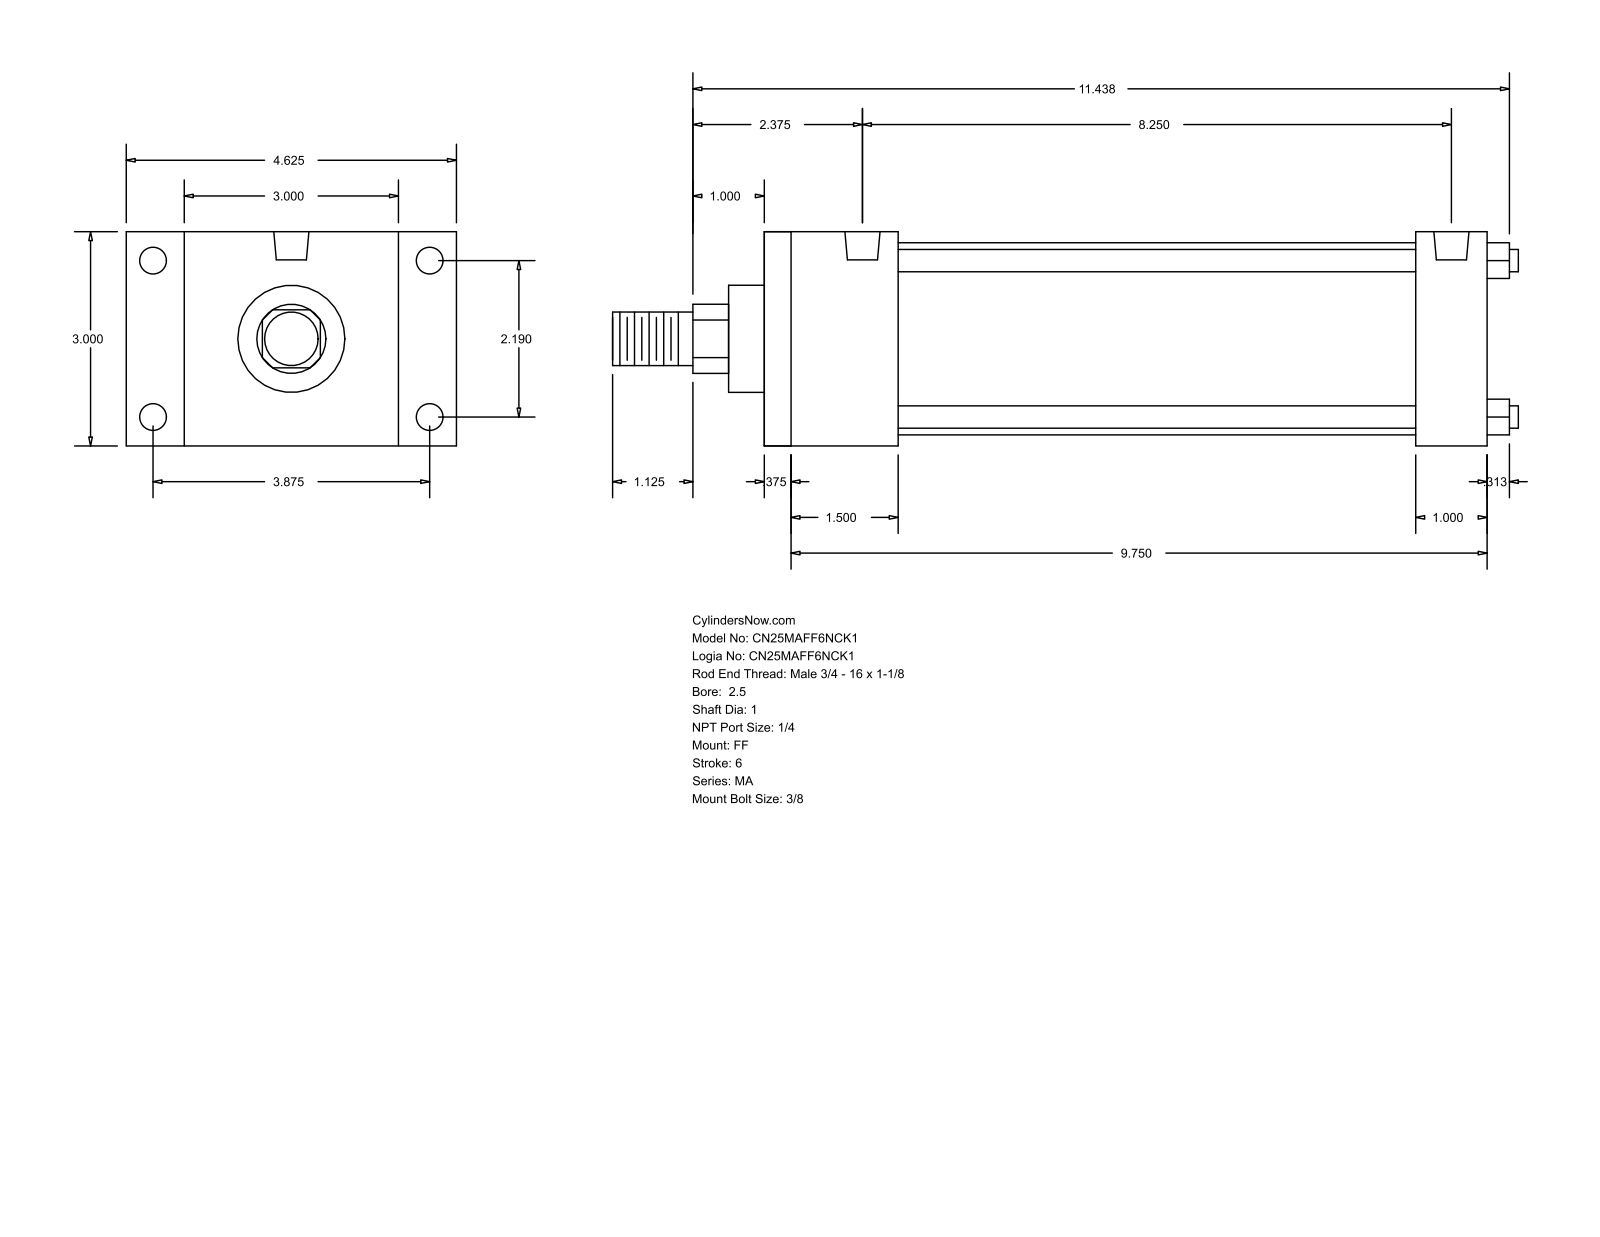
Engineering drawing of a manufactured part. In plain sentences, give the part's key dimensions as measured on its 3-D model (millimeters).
The part is named "MA_FF__0250_1". Its 3-D file was written by "GSSL Pune (CONFIG_CONTROL_DESIGN)". It is 0 solids with 92 faces: 64 planar, 28 cylindrical and 0 other. Overall it measures 322.26 by 117.47 by 76.2 millimeters. Round holes: 4 of diameter 7.94, 4 of diameter 9.53, 2 of diameter 12.49. Round bosses or shafts: 4 of diameter 7.94, 1 of diameter 68.33, 1 of diameter 38.1, 1 of diameter 25.4, 1 of diameter 19.05. Partial cylindrical surfaces (rounded edges, fillets, slot ends): 1 of radius 12.29. The main face-to-face distances are 76.2, 257.17, 247.65, 9.52, 25.39, 47.63, 231.78, 38.11, 222.26, 184.15. The hole center spacings are 55.62, 98.42, 113.05, 209.55.
